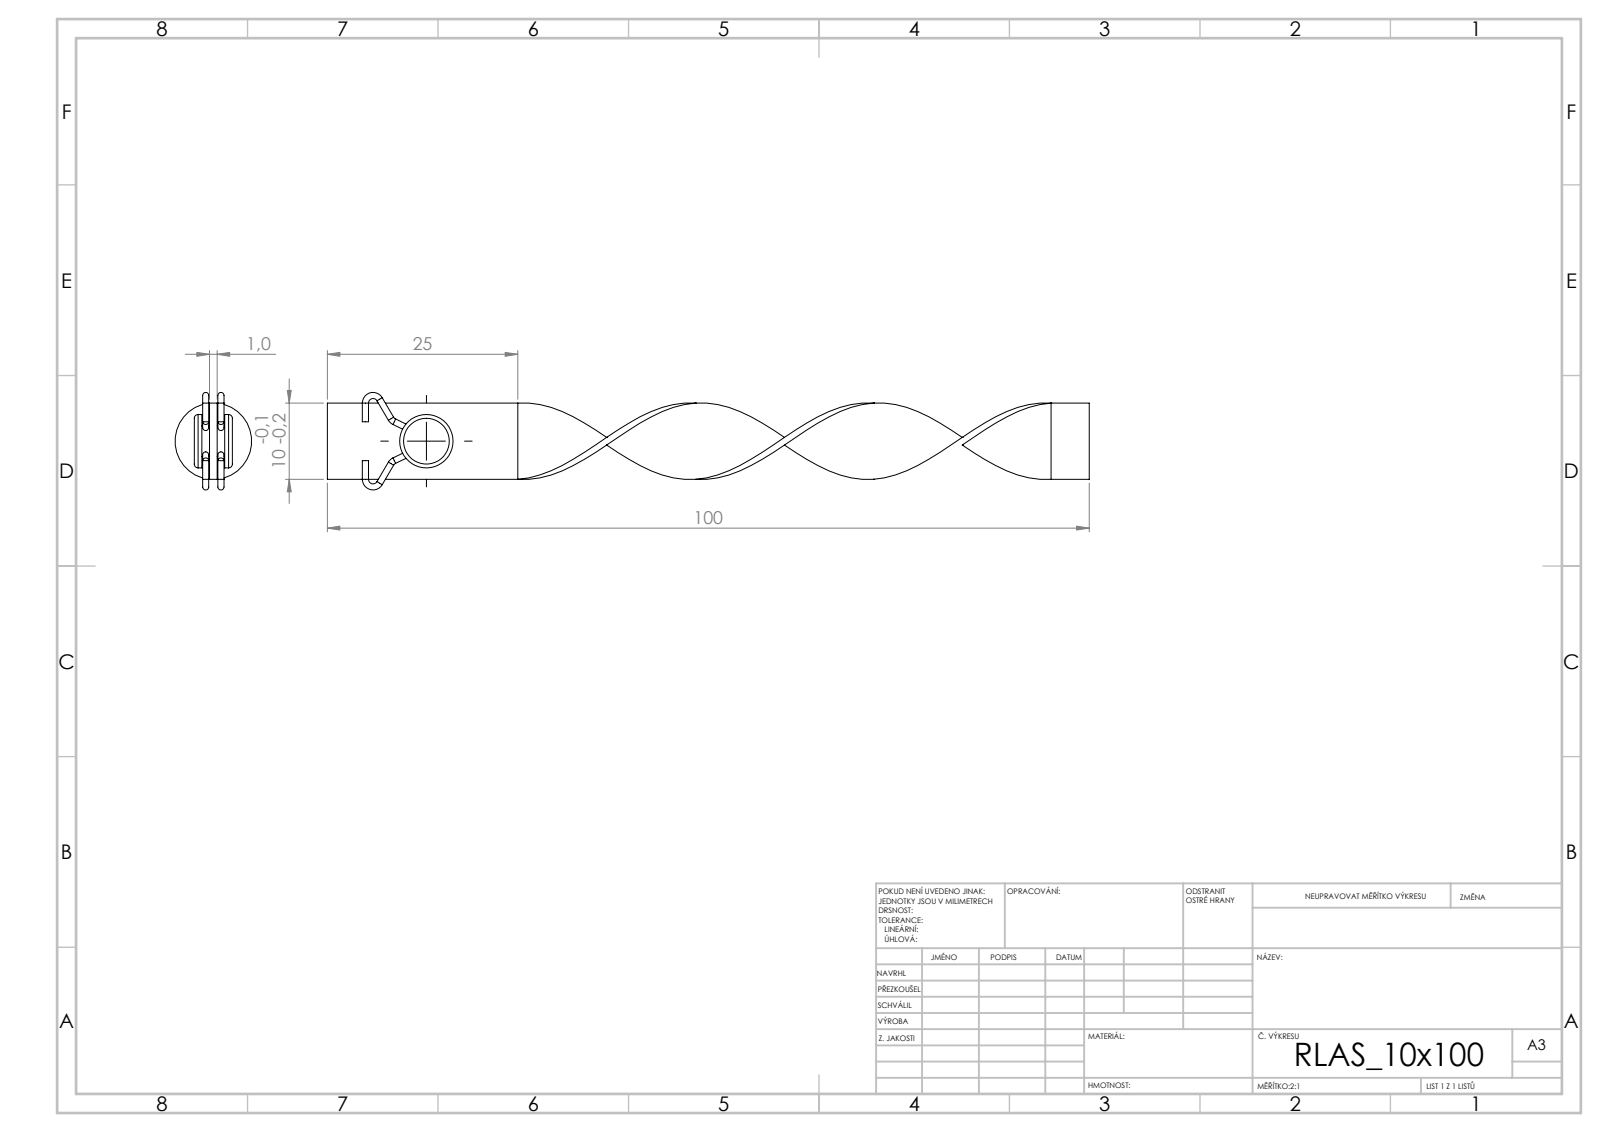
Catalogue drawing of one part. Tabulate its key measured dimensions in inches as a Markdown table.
| quantity | value |
| --- | --- |
| STEP written by | SolidWorks 2019 (CONFIG_CONTROL_DESIGN) |
| units | inches |
| bodies | 3 solids, 90 faces (18 planar, 40 cylindrical, 32 other) |
| overall size | 3.937 × 0.504 × 0.396 |
| volume | 0.069 in³ |
| surface area | 4.12 in² |
| round bosses / shafts (diameter × count) | 0.031 × 14, 0.276 × 1, 0.157 × 1 |
| main face-to-face distances | 0.039, 0.079, 0.118, 0.157, 0.394, 0.197, 3.937, 0.096, 0.297, 0.201 |
